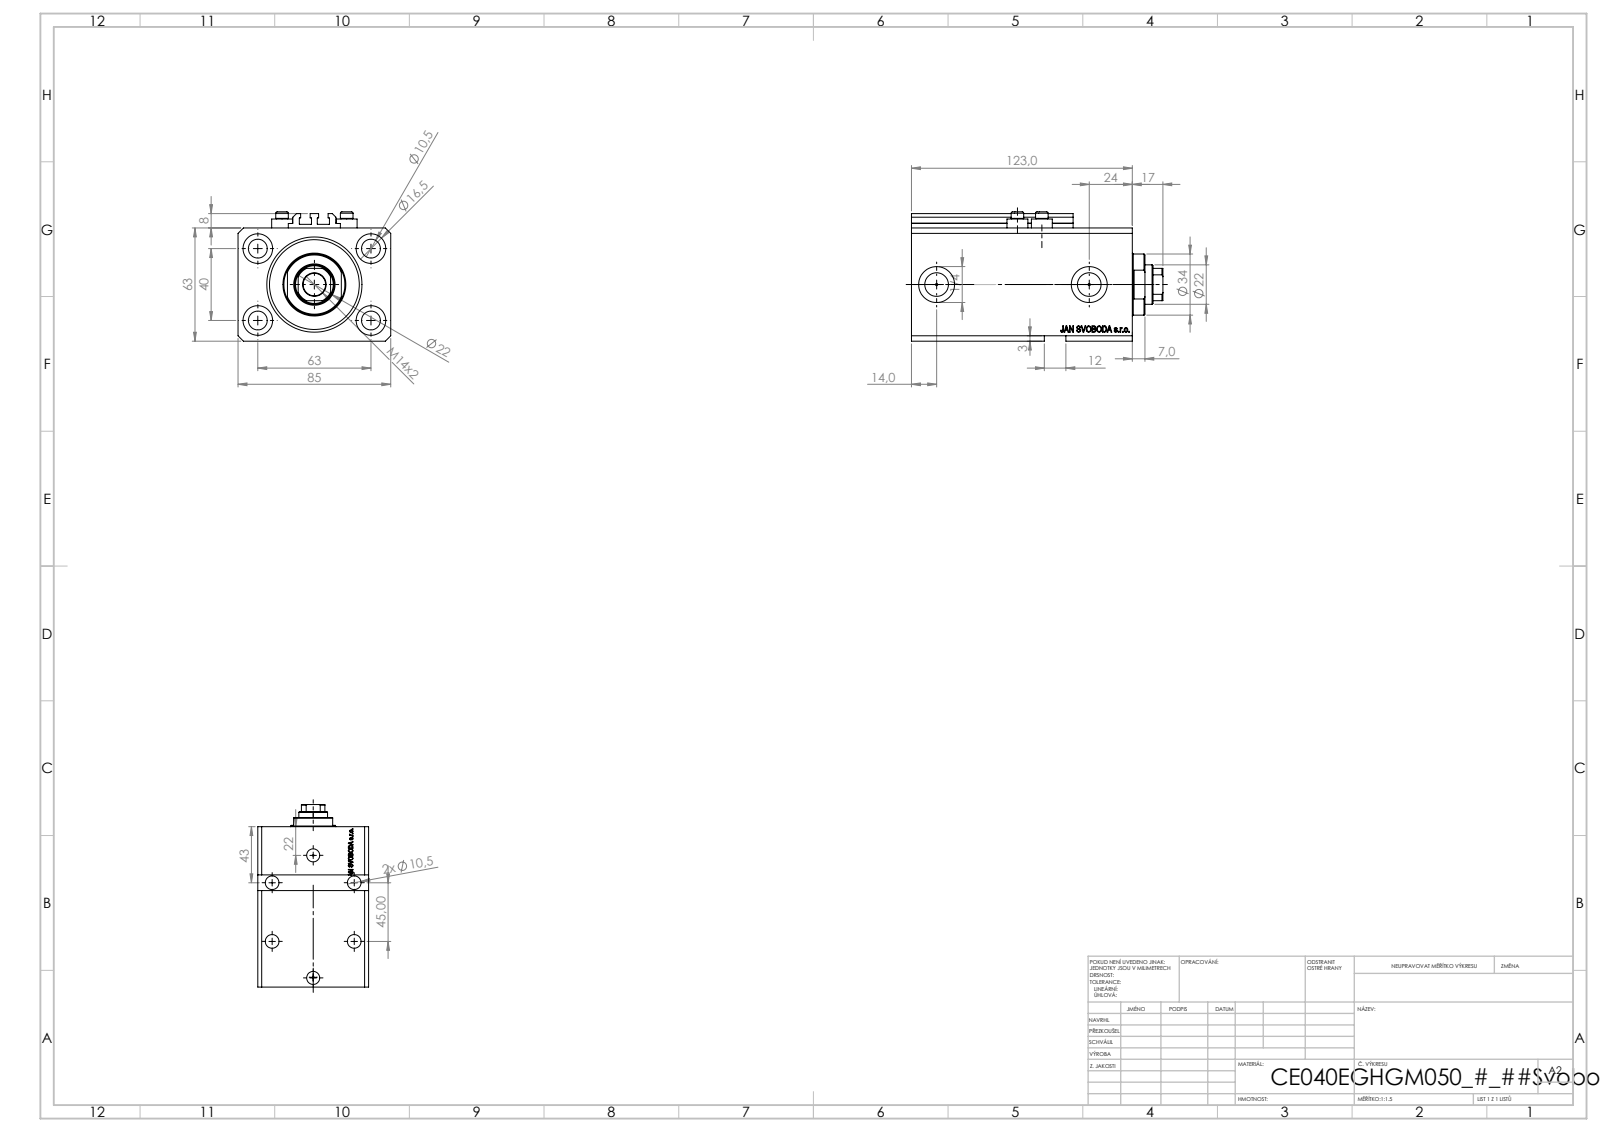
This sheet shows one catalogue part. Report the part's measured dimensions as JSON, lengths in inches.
{"part_name": "V250CE_VC_E; V250CE_E_Body; V250CE_C_VCP; ALLEN BOLT V250CE", "step_written_by": "SolidWorks 2019 (CONFIG_CONTROL_DESIGN)", "units": "inches", "bodies": {"solids": 8, "faces": 1107, "planar": 535, "cylindrical": 146, "other": 426}, "overall_size": [5.512, 3.346, 2.835], "volume_in3": 33.97, "surface_area_in2": 185, "round_holes": [[0.413, 8], [0.049, 4], [0.157, 4], [0.65, 4], [0.394, 2], [0.518, 2], [0.787, 2], [0.492, 1], [0.866, 1], [1.575, 1], [2.087, 1]], "round_bosses_or_shafts": [[0.457, 4], [0.276, 4], [1.339, 1]], "partial_cylinders_radius": [[0.008, 10], [0.413, 1]], "face_to_face_distances": [2.48, 3.346, 4.843, 0.669, 4.173, 0.449, 3.724, 4.394, 0.118, 2.205], "hole_center_spacings": [1.469, 2.48, 0.535, 0.606, 0.983, 1.084, 1.324, 1.417]}
